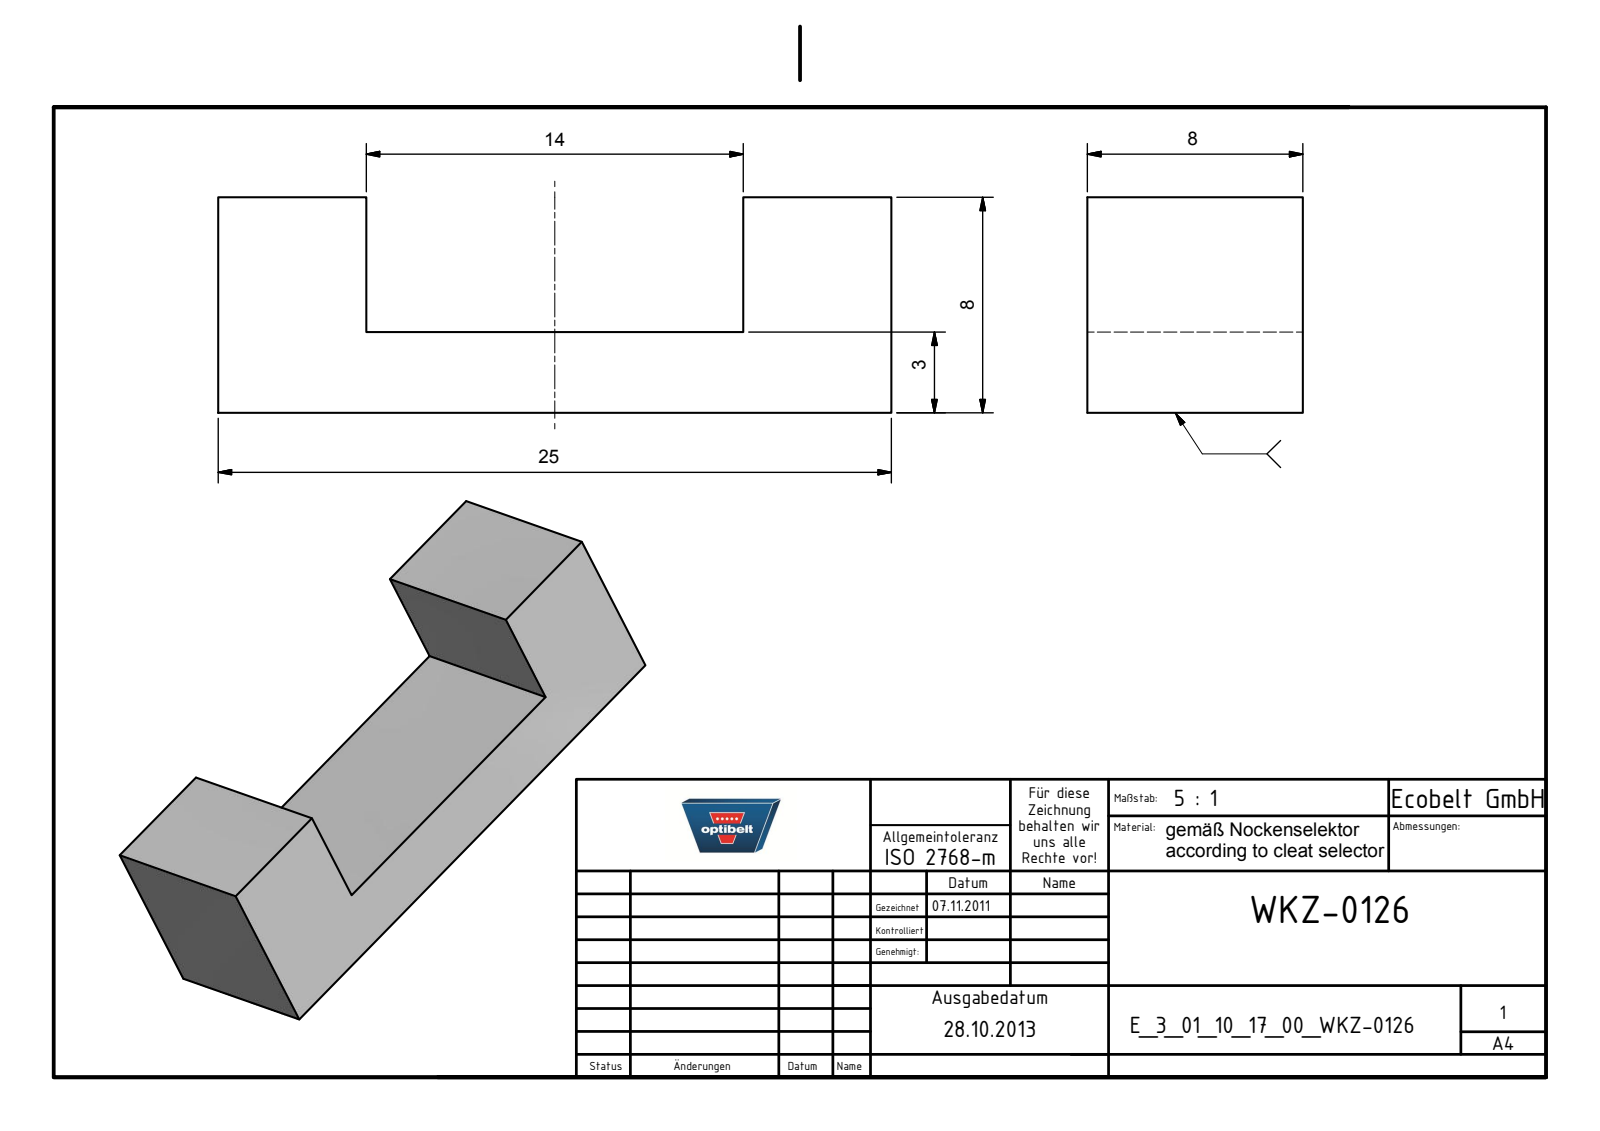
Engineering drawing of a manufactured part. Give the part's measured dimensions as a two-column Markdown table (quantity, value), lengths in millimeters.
| quantity | value |
| --- | --- |
| part name | E_3_01_10_17_00_WKZ-0126 |
| STEP written by | Autodesk Inventor 2025 (AUTOMOTIVE_DESIGN) |
| units | millimeters |
| bodies | 1 solid, 10 faces (10 planar, 0 cylindrical, 0 other) |
| overall size | 25 × 8 × 8 |
| volume | 1 040 mm³ |
| surface area | 868 mm² |
| main face-to-face distances | 8, 3, 5, 5.5, 19.5, 25, 14 |
